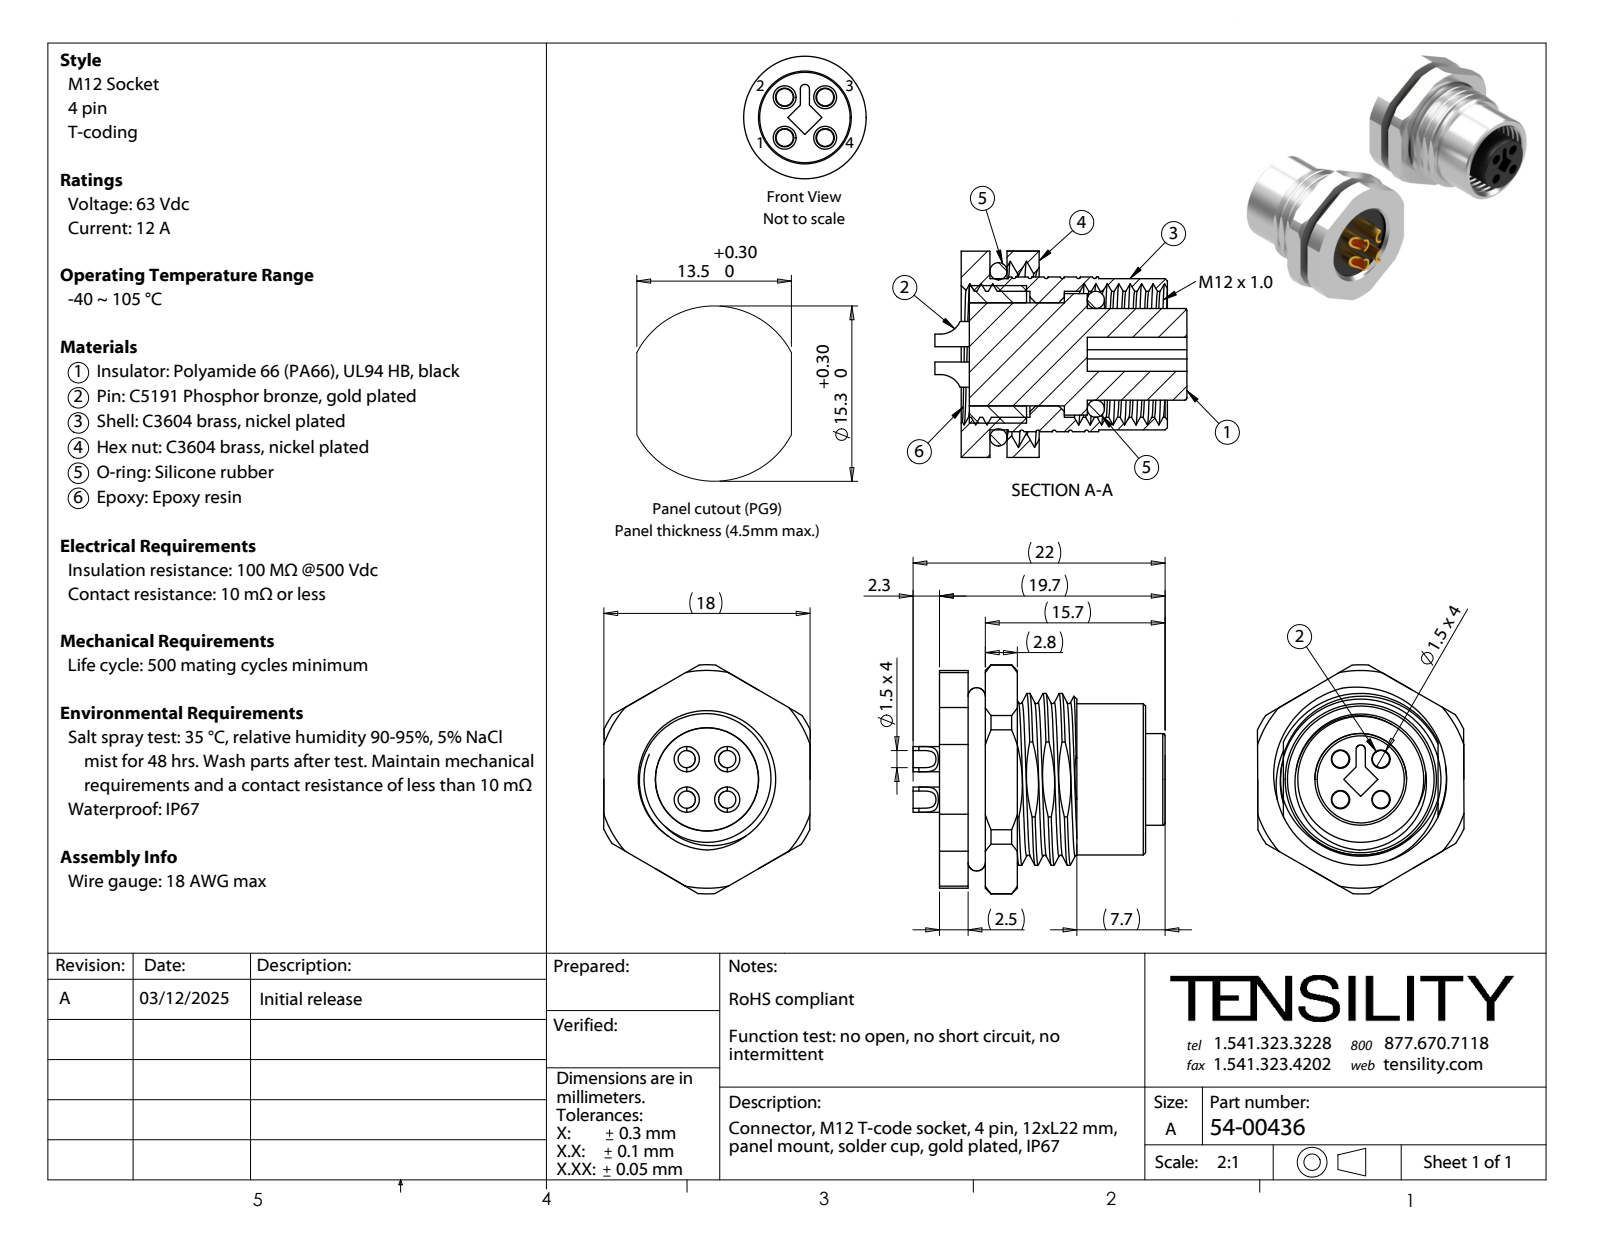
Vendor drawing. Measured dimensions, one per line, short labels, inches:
name: 54-00436-06; 54-00436_revA; 54-00436-03; 54-00436-01 (+3 more)
written by: SolidWorks 2021 (CONFIG_CONTROL_DESIGN)
unit: in
bodies: 10 solids, 320 faces (105 planar, 128 cylindrical, 87 other)
size: 0.866 × 0.787 × 0.71
volume: 0.177 in³; area: 8.895 in²
holes: 4× ⌀0.059, 4× ⌀0.063, 1× ⌀0.354, 1× ⌀0.433, 1× ⌀0.551
bosses: 4× ⌀0.087, 1× ⌀0.52, 1× ⌀0.472, 1× ⌀0.417, 1× ⌀0.315
rounds: 2× R0.073, 1× R0.016, 1× R0.295, 1× R0.374, 1× R0.394
face distances: 0.098, 0.709, 0.13, 0.197, 0.028, 0.071, 0.157, 0.169, 0.059, 0.268
hole spacings: 0.098, 0.139, 0.197
